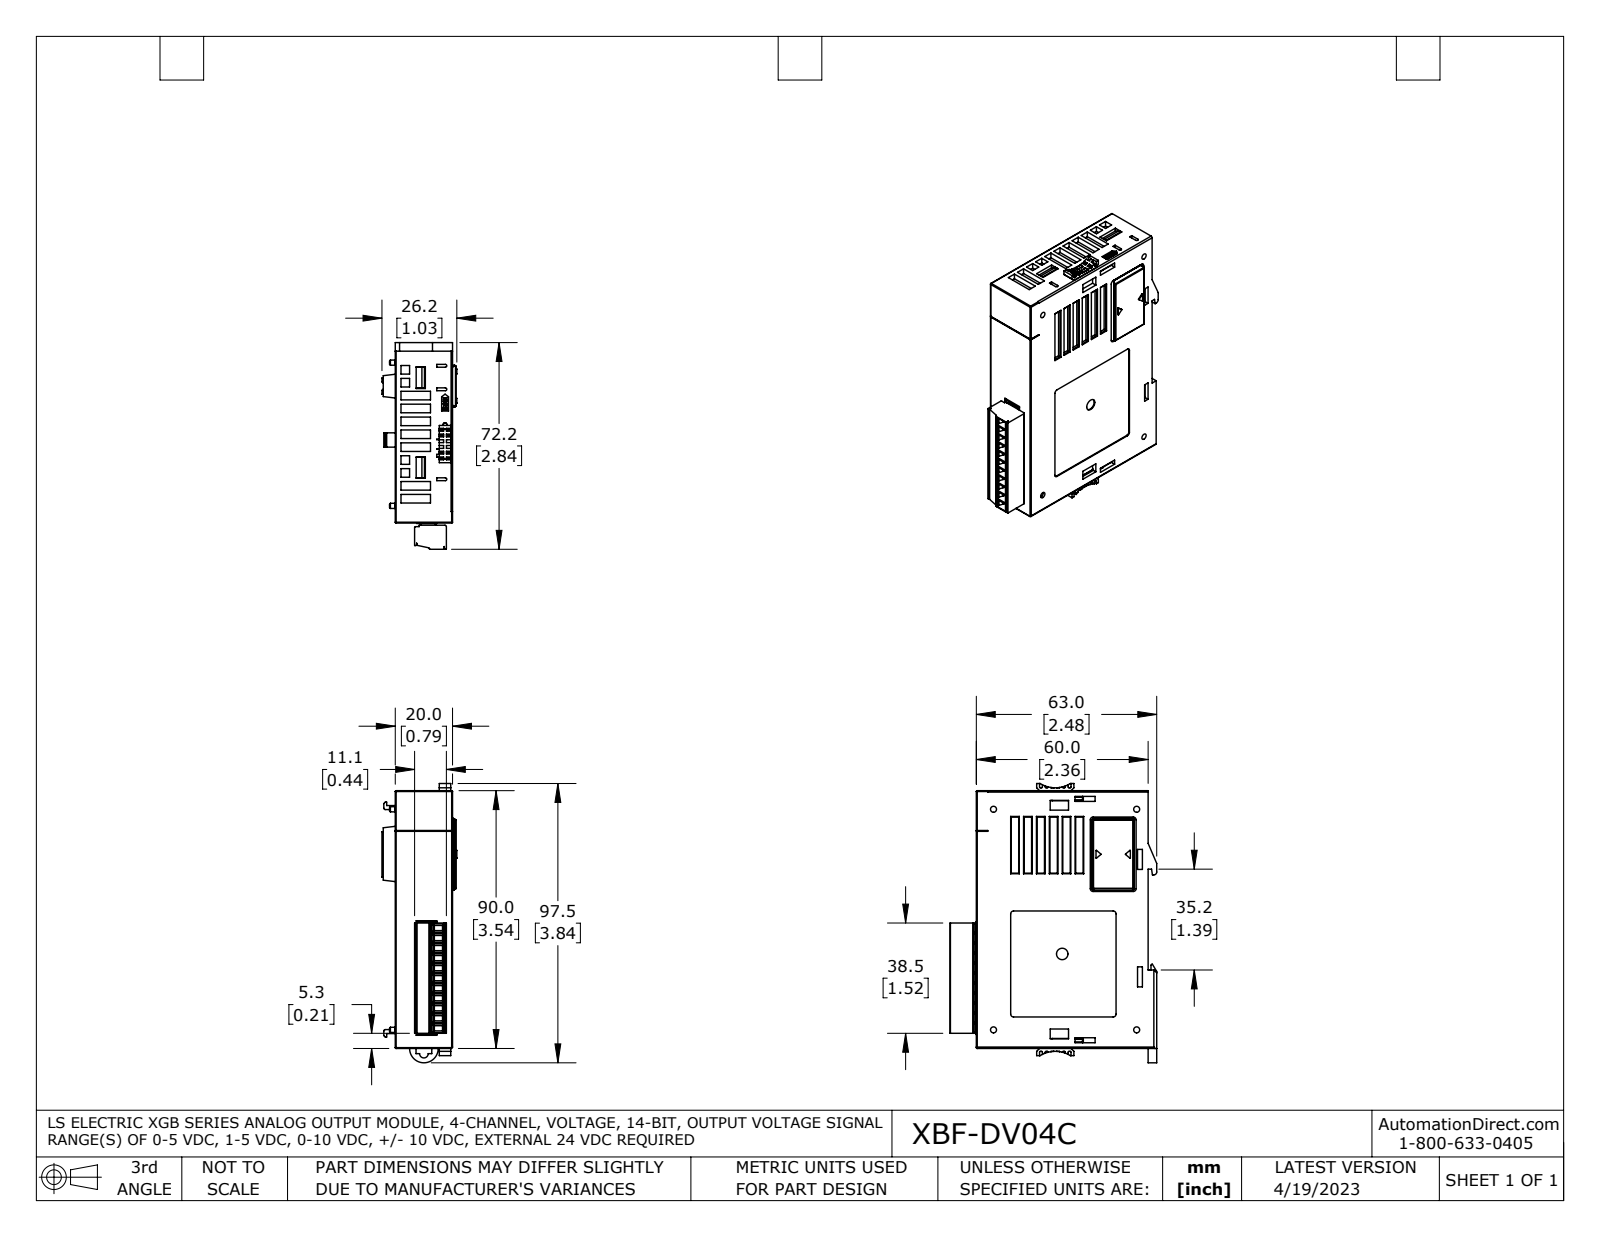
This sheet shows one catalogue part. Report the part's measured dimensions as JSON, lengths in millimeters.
{"part_name": "XBF-DV04C nc coord fxt", "step_written_by": "SolidWorks 2021 (AUTOMOTIVE_DESIGN)", "units": "millimeters", "bodies": {"solids": 1, "faces": 2872, "planar": 2161, "cylindrical": 494, "other": 217}, "overall_size": [97.5, 72.2, 26.2], "volume_mm3": 109200, "surface_area_mm2": 30050, "round_holes": [[1.2, 11], [2.7, 11], [2.9, 11], [2.1, 4], [4, 1]], "round_bosses_or_shafts": [[2.8, 11], [1.8, 4], [2, 2]], "partial_cylinders_radius": [[0.3, 76], [0.1, 74], [0.2, 50], [0.5, 28], [1, 11], [1.6, 11], [1.8, 11], [0.8, 6]], "face_to_face_distances": [20, 0.8, 19.7, 1, 60, 19, 1.5, 1.3, 2, 18.7], "hole_center_spacings": [3.5, 7, 10.5, 14, 17.5, 21, 24.5, 28]}
